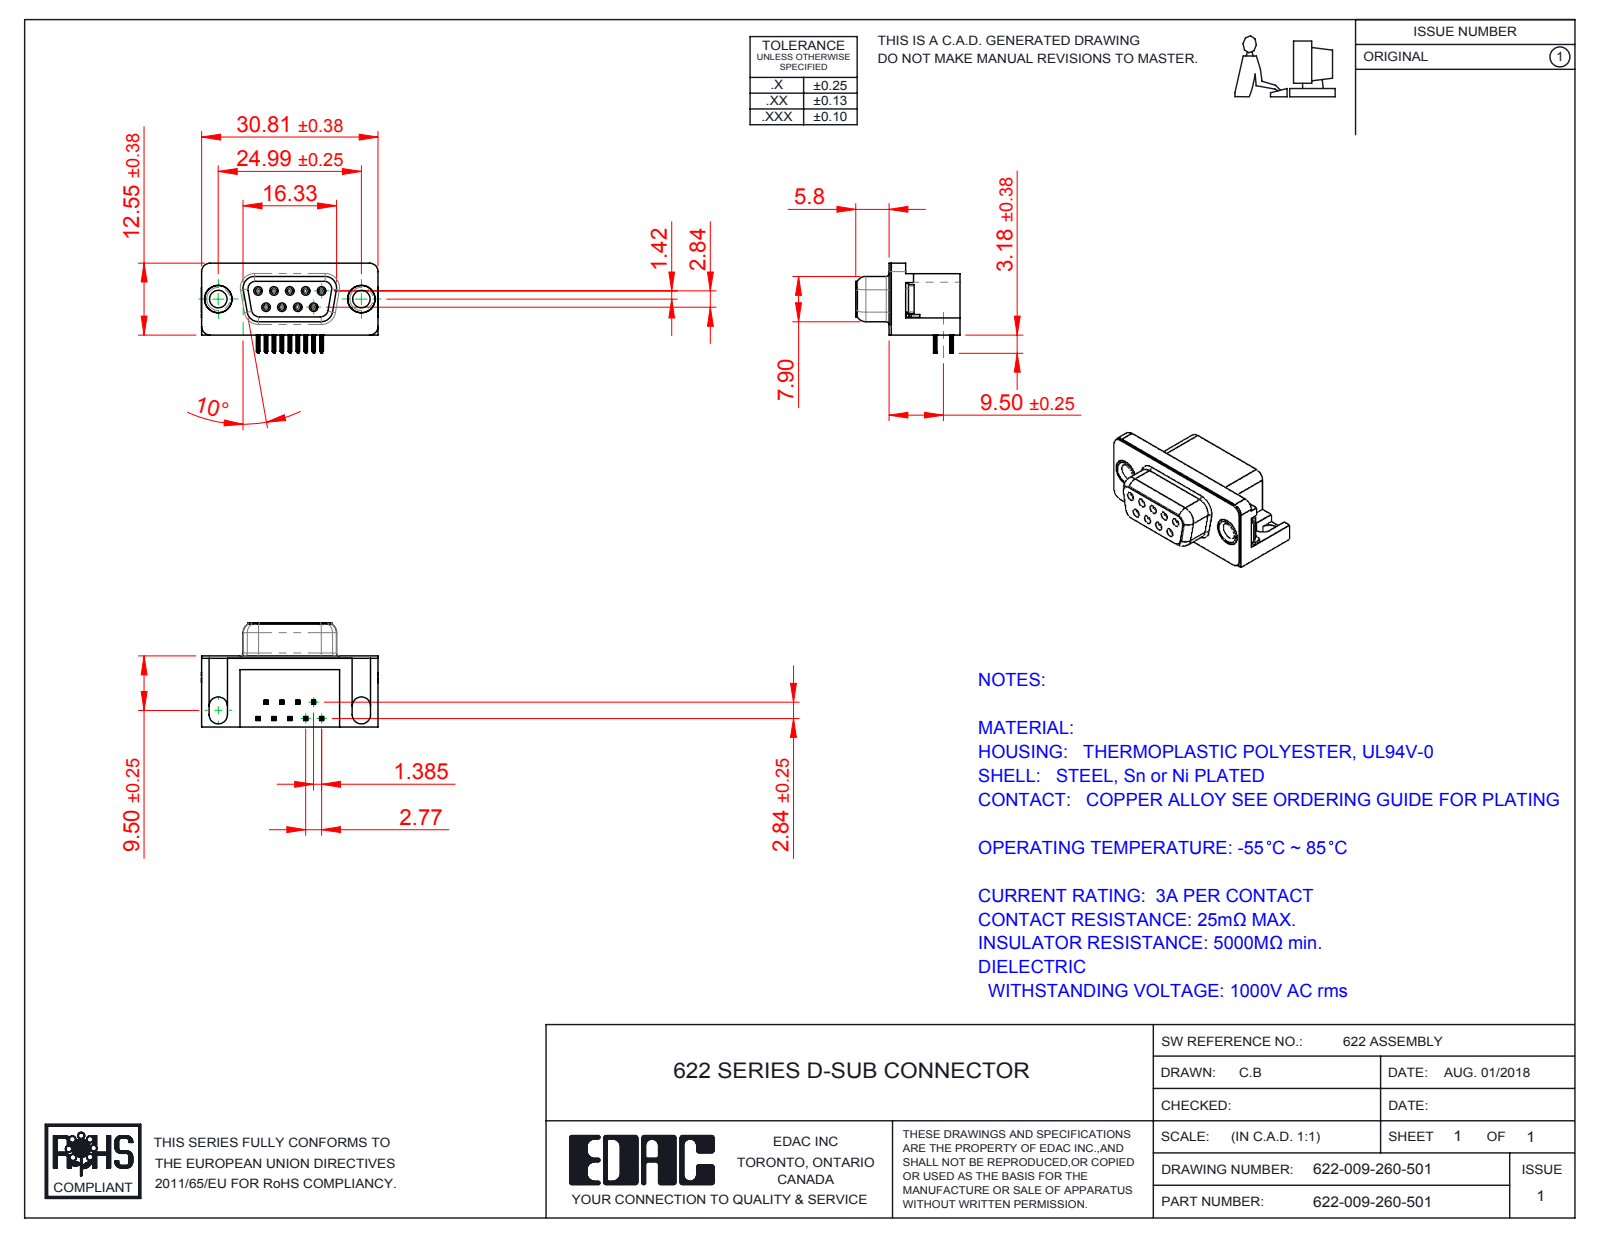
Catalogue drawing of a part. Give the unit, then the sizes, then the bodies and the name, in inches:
Units: inches
Overall size (bounding box): 1.216 × 0.717 × 0.619
Round holes (diameter × count): ⌀0.031 ×9, ⌀0.035 ×9, ⌀0.12 ×2, ⌀0.157 ×2, ⌀0.189 ×2, ⌀0.197 ×2
Round bosses / shafts (diameter × count): ⌀0.047 ×9, ⌀0.193 ×2, ⌀0.187 ×2, ⌀0.152 ×2
Partial cylindrical surfaces — rounded edges, fillets, slot ends (radius × count): R0.004 ×72, R0.006 ×36, R0.014 ×18, R0.039 ×18, R0.013 ×9, R0.01 ×8, R0.053 ×8, R0.063 ×8
Main face-to-face distances: 0.016, 0.472, 0.488, 0.114, 0.098, 0.244, 0.407, 0.014, 0.374, 0.421
Hole centre spacings: 0.124, 0.109, 0.218, 0.198, 0.198, 0.327, 0.294, 0.295
Volume: 0.224 in³ · Surface area: 7.559 in²
Bodies: 15 solids, 1528 faces (684 planar, 394 cylindrical, 450 other)
Part name (STEP PRODUCT): 622 Thru Hole Rivet; 622 Non Board Mount; 622 Socket Bottom; 622 Housing_9 Socket (+3 more)
STEP written by: SolidWorks 2016 (CONFIG_CONTROL_DESIGN)
